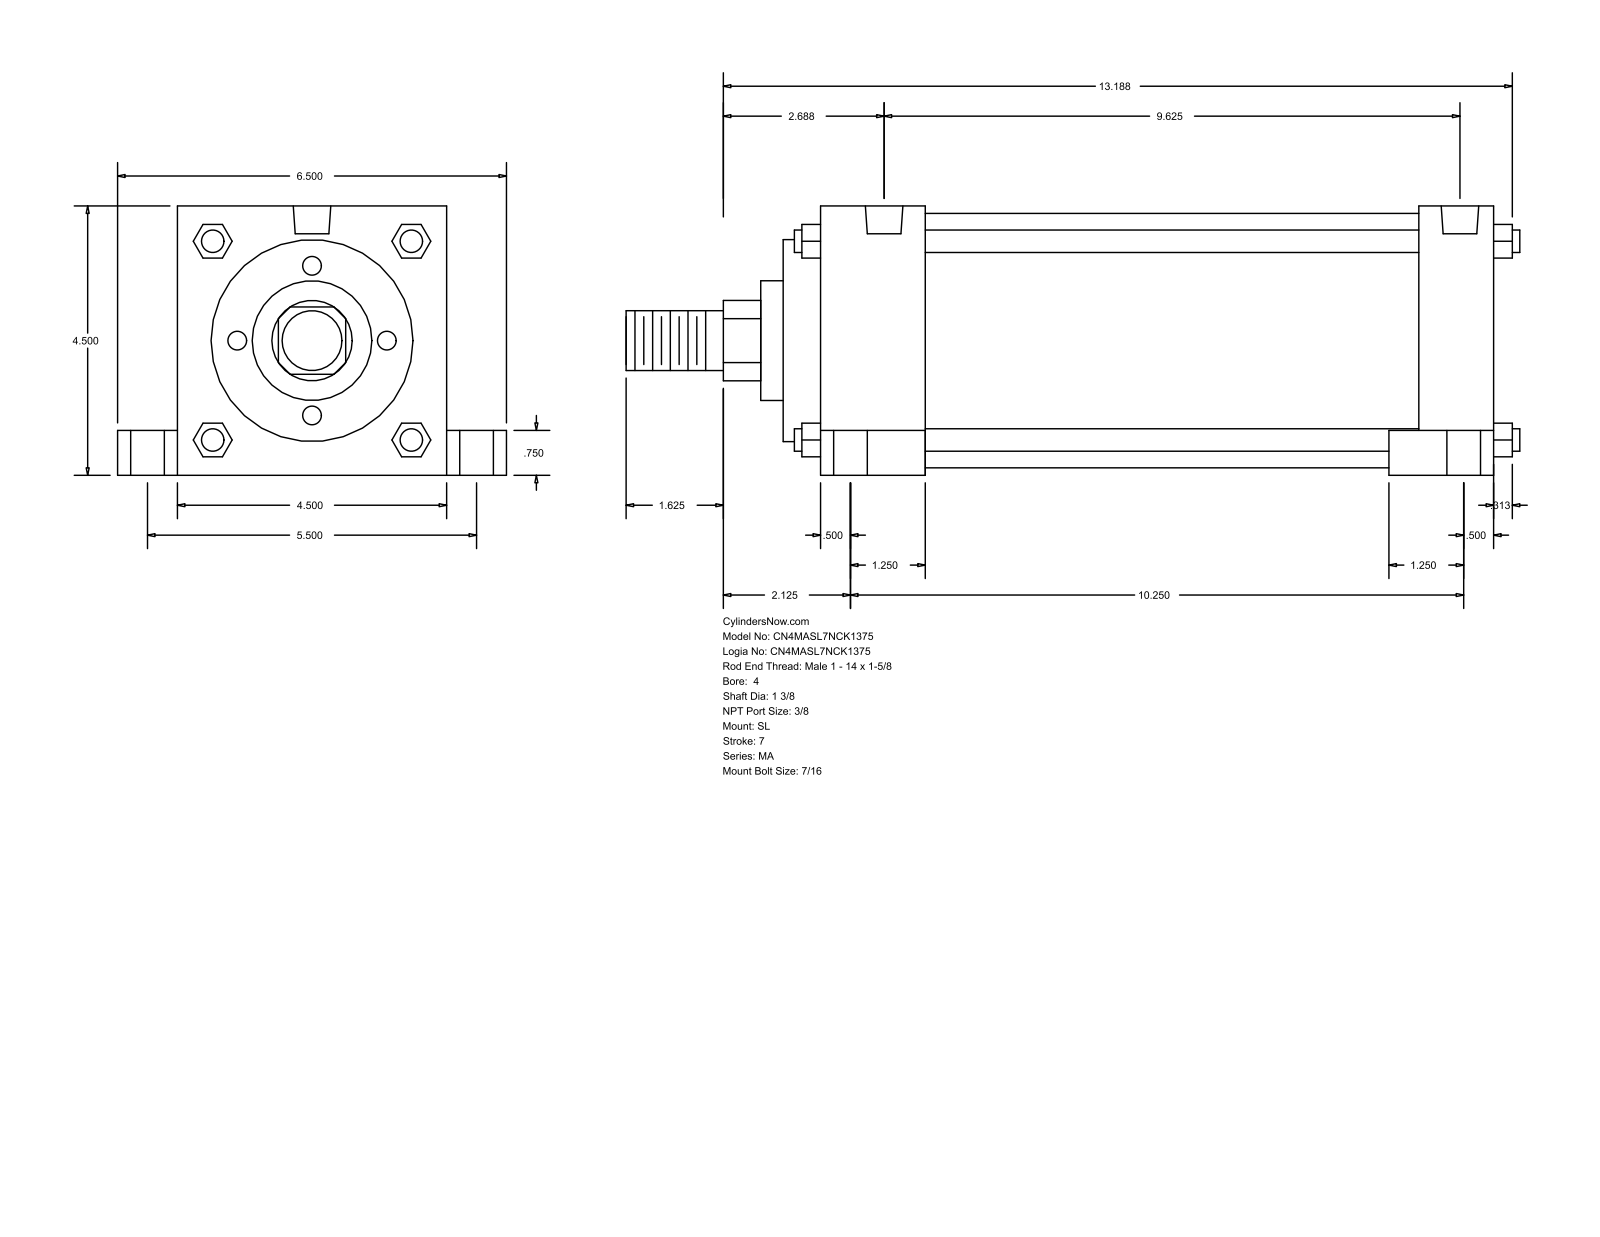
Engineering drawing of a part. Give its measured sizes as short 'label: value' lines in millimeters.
name: MA_SL__0400_1.375
written by: GSSL Pune (CONFIG_CONTROL_DESIGN)
unit: mm
bodies: 0 solids, 150 faces (113 planar, 37 cylindrical, 0 other)
size: 379.41 × 165.1 × 114.3
holes: 4× ⌀11.11, 4× ⌀14.29, 4× ⌀20.64, 2× ⌀15.93
bosses: 4× ⌀9.53, 1× ⌀107.95, 1× ⌀85.72, 1× ⌀50.8, 1× ⌀34.92, 1× ⌀25.4
rounds: 1× R17.06
face distances: 114.3, 285.75, 209.55, 301.62, 15.87, 60.32, 44.45, 241.3, 269.87, 254
hole spacings: 69.87, 70.14, 71.29, 72.4, 139.7, 234.95, 251.2, 255.78
